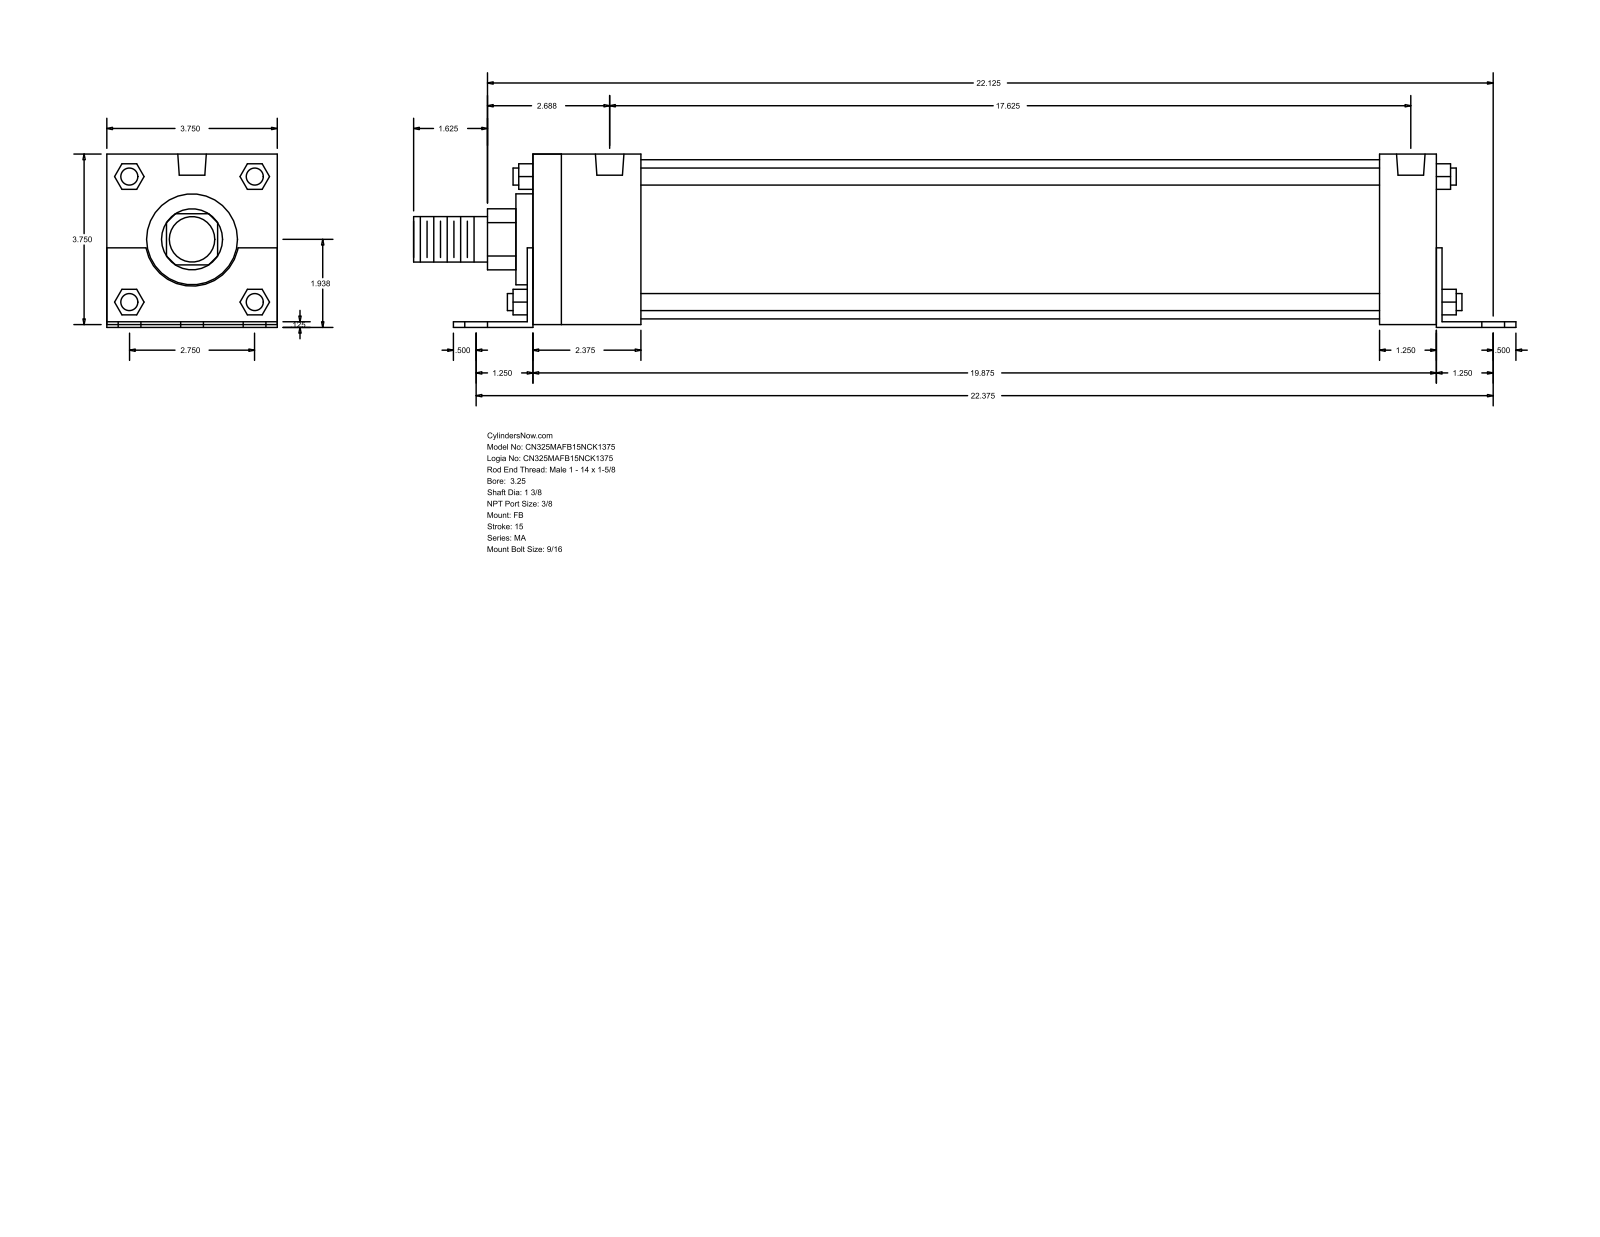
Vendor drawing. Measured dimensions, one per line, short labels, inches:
name: MA_FB__0325_1.375
written by: GSSL Pune (CONFIG_CONTROL_DESIGN)
unit: in
bodies: 0 solids, 140 faces (105 planar, 35 cylindrical, 0 other)
size: 24.25 × 3.813 × 3.75
holes: 6× ⌀0.563, 4× ⌀0.437, 2× ⌀0.627
bosses: 4× ⌀0.375, 1× ⌀3.5, 1× ⌀2, 1× ⌀1.375, 1× ⌀1
rounds: 1× R0.672, 1× R1.03
face distances: 3.75, 0.125, 0.063, 3.812, 0.062, 3.687, 20, 19.875, 1.25, 1.375
hole spacings: 1.375, 22.417, 22.375, 2.275, 2.427, 2.75, 3.243, 3.414
